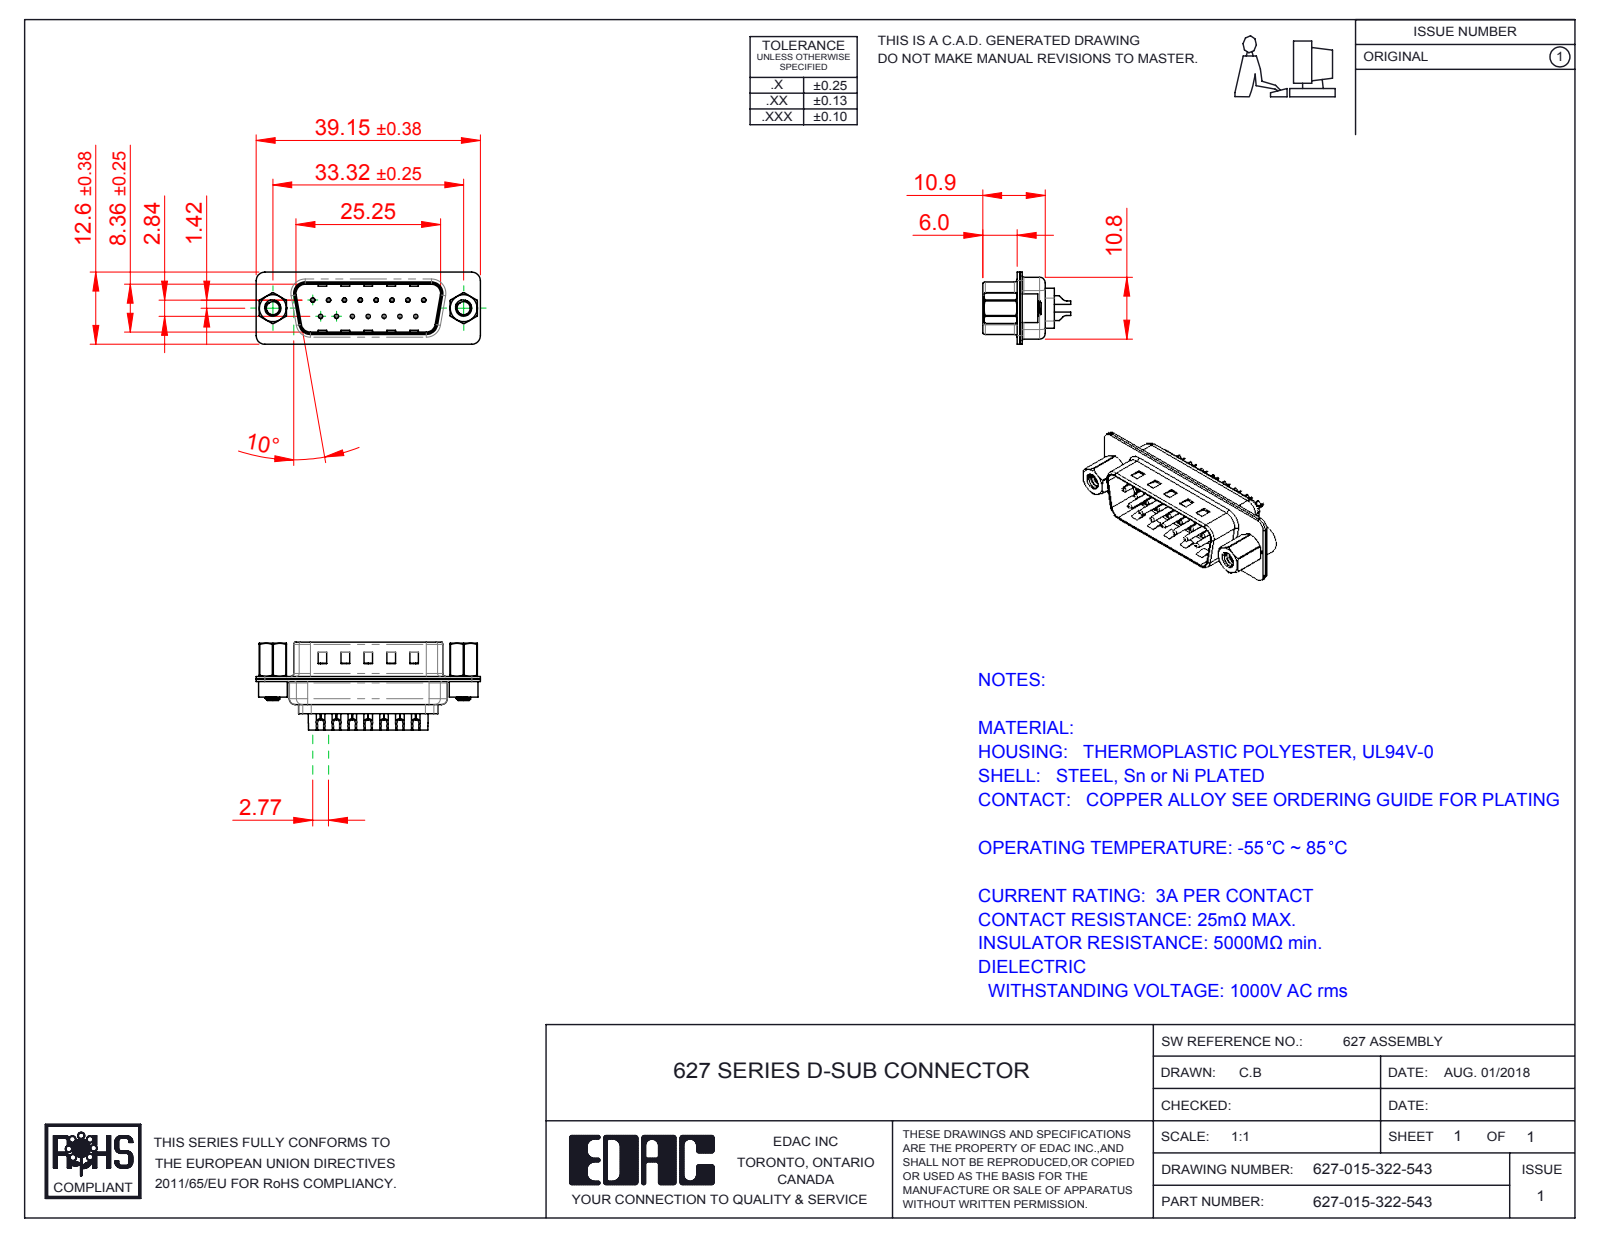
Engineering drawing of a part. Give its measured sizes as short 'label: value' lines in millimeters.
name: 627 Shell Front_15 Contacts; 627 Contact Row 2_22L; 627 Shell Rear_15 Contacts; 627-015-322-543 (+4 more)
written by: SolidWorks 2016 (CONFIG_CONTROL_DESIGN)
unit: mm
bodies: 22 solids, 1426 faces (371 planar, 640 cylindrical, 415 other)
size: 39.15 × 15.35 × 12.6
volume: 2 050 mm³; area: 5 912 mm²
holes: 15× ⌀0.35, 15× ⌀1.1, 15× ⌀1.6, 2× ⌀2.26, 2× ⌀2.29, 2× ⌀4, 2× ⌀4.8
bosses: 15× ⌀2, 15× ⌀1.5, 15× ⌀0.75, 2× ⌀5, 2× ⌀4.9, 2× ⌀2.79
rounds: 16× R1.5, 12× R2, 8× R0.5, 8× R1.6, 6× R1, 4× R0.25, 4× R0.6, 4× R0.65
face distances: 0.4, 0.45, 0.9, 0.82, 9.58, 8.76, 1.5, 1.4, 6.5, 5.6
hole spacings: 3.16, 2.77, 5.54, 8.31, 11.08, 5.03, 5.04, 7.48
